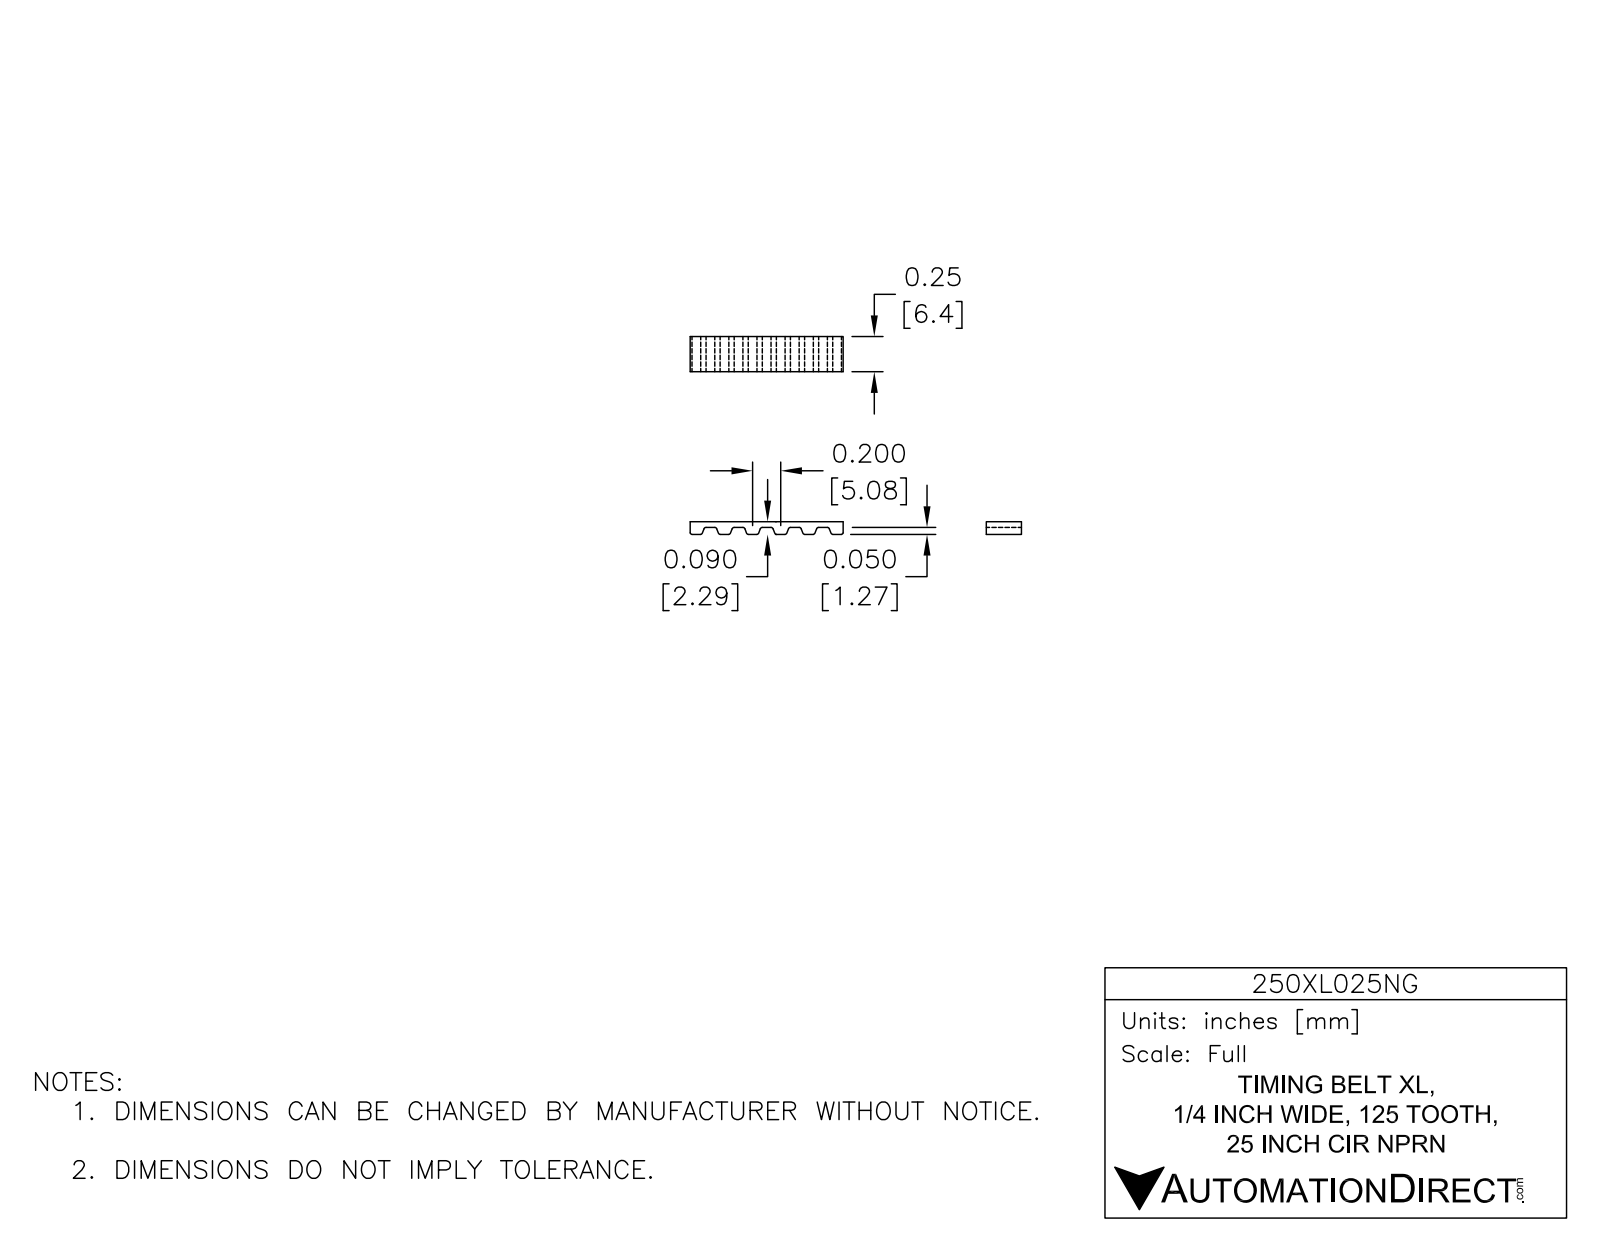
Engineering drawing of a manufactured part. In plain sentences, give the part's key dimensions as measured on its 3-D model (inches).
The part is named "250XL025NG". Its 3-D file was written by "SolidWorks 2014 (AUTOMOTIVE_DESIGN)". It is 1 solid with 1039 faces: 458 planar, 581 cylindrical and 0 other. Overall it measures 10.788 by 3 by 0.25 inches. Its volume is 0.34 cubic inches and its surface area 16.88 square inches. Partial cylindrical surfaces (rounded edges, fillets, slot ends): 500 of radius 0.015, 2 of radius 1.46, 2 of radius 1.5. The main face-to-face distances are 3, 0.04, 2.96, 0.25, 2.92, 2.87, 0.09, 2.91, 0.05, 0.359.
